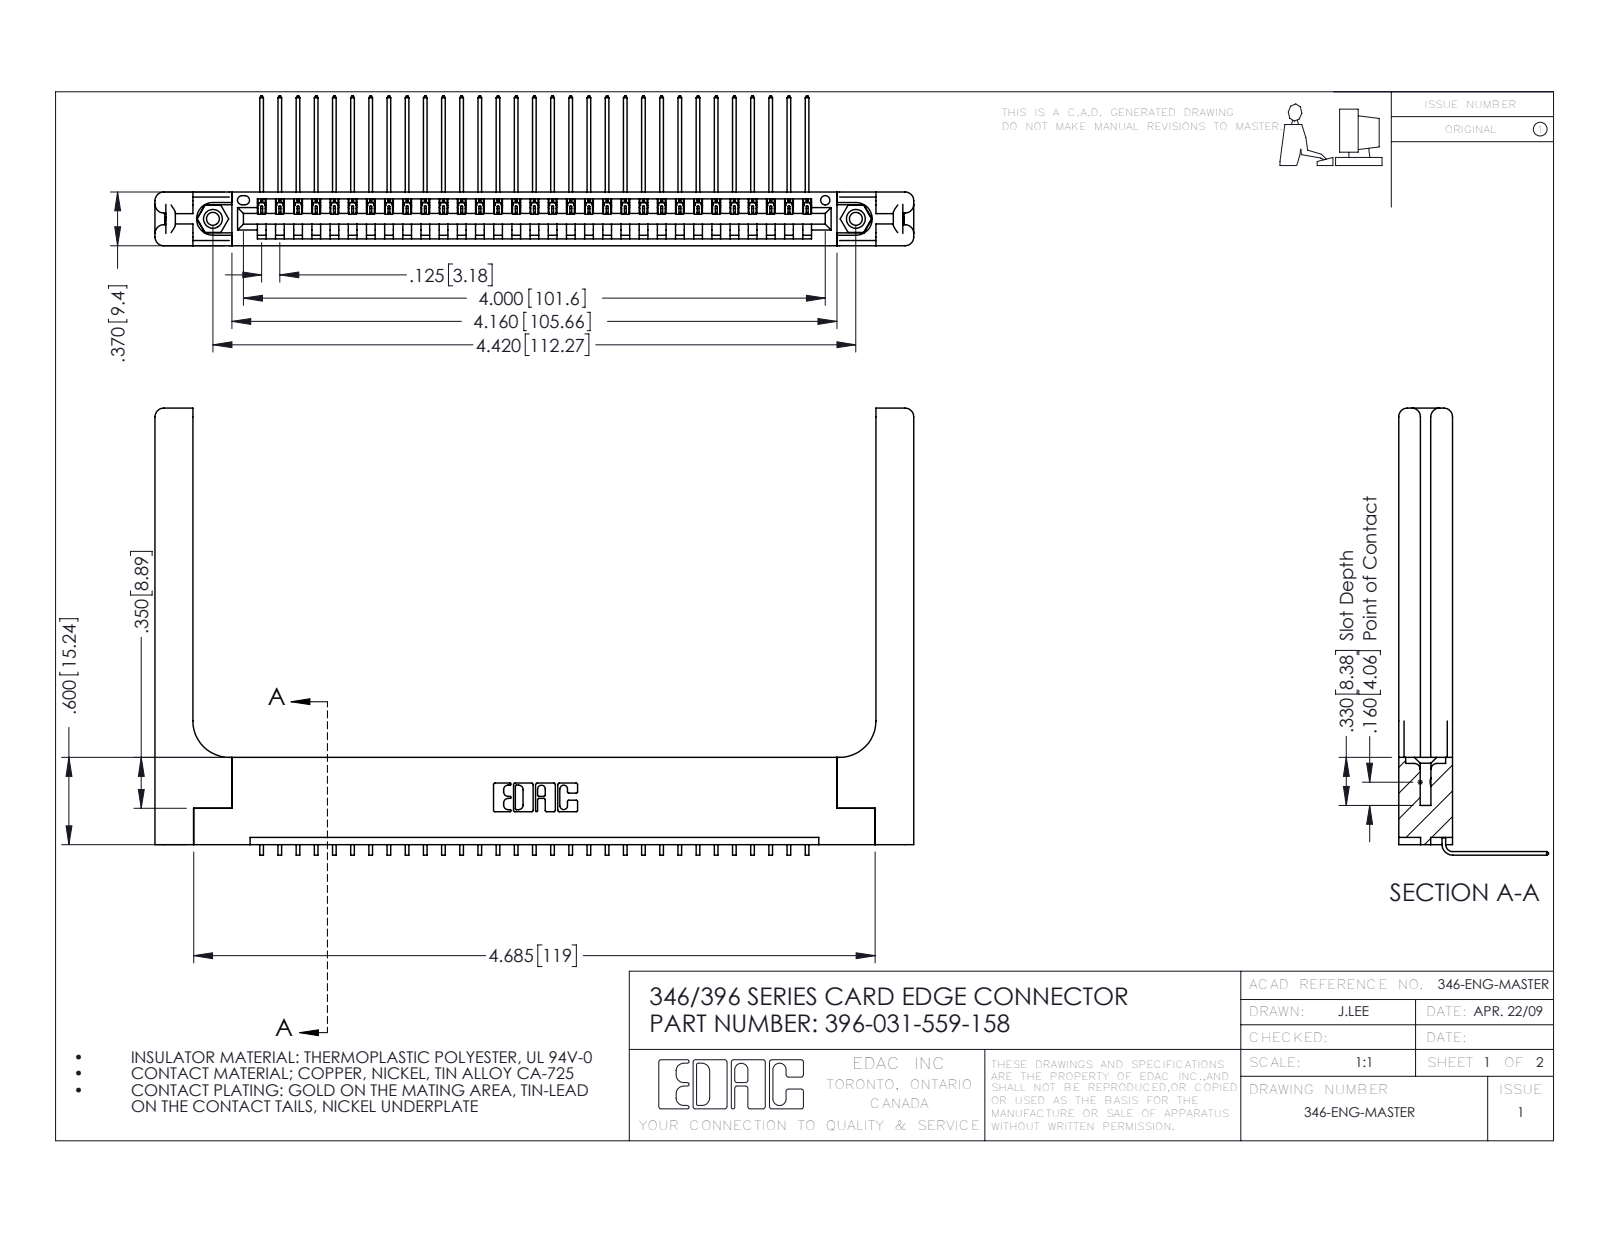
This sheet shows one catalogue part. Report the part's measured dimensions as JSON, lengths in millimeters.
{"part_name": "345-250-001_345-250-001-102; 345-292-001_558 559 Tail - 1; 346 Part_Flush Mounting Lugs - 0.156 Dia-TH; 346-220-058_345-220-058 (+1 more)", "step_written_by": "SolidWorks 2016 (CONFIG_CONTROL_DESIGN)", "units": "millimeters", "bodies": {"solids": 36, "faces": 2238, "planar": 1526, "cylindrical": 652, "other": 60}, "overall_size": [132.5, 78.1, 26.2], "volume_mm3": 20220, "surface_area_mm2": 21550, "round_holes": [[2.3, 2], [3.2, 2], [4, 2], [1.6, 1]], "round_bosses_or_shafts": [[3.9, 2]], "partial_cylinders_radius": [[0.2, 62], [0.3, 22], [1.5, 16], [0.2, 6], [0.8, 6], [0.7, 3], [0.8, 2], [0.8, 2]], "face_to_face_distances": [9.4, 1.8, 1.2, 8.2, 3.8, 3.8, 0.6, 6.4, 7.6, 5.6], "hole_center_spacings": [6.2, 107, 112.3]}
